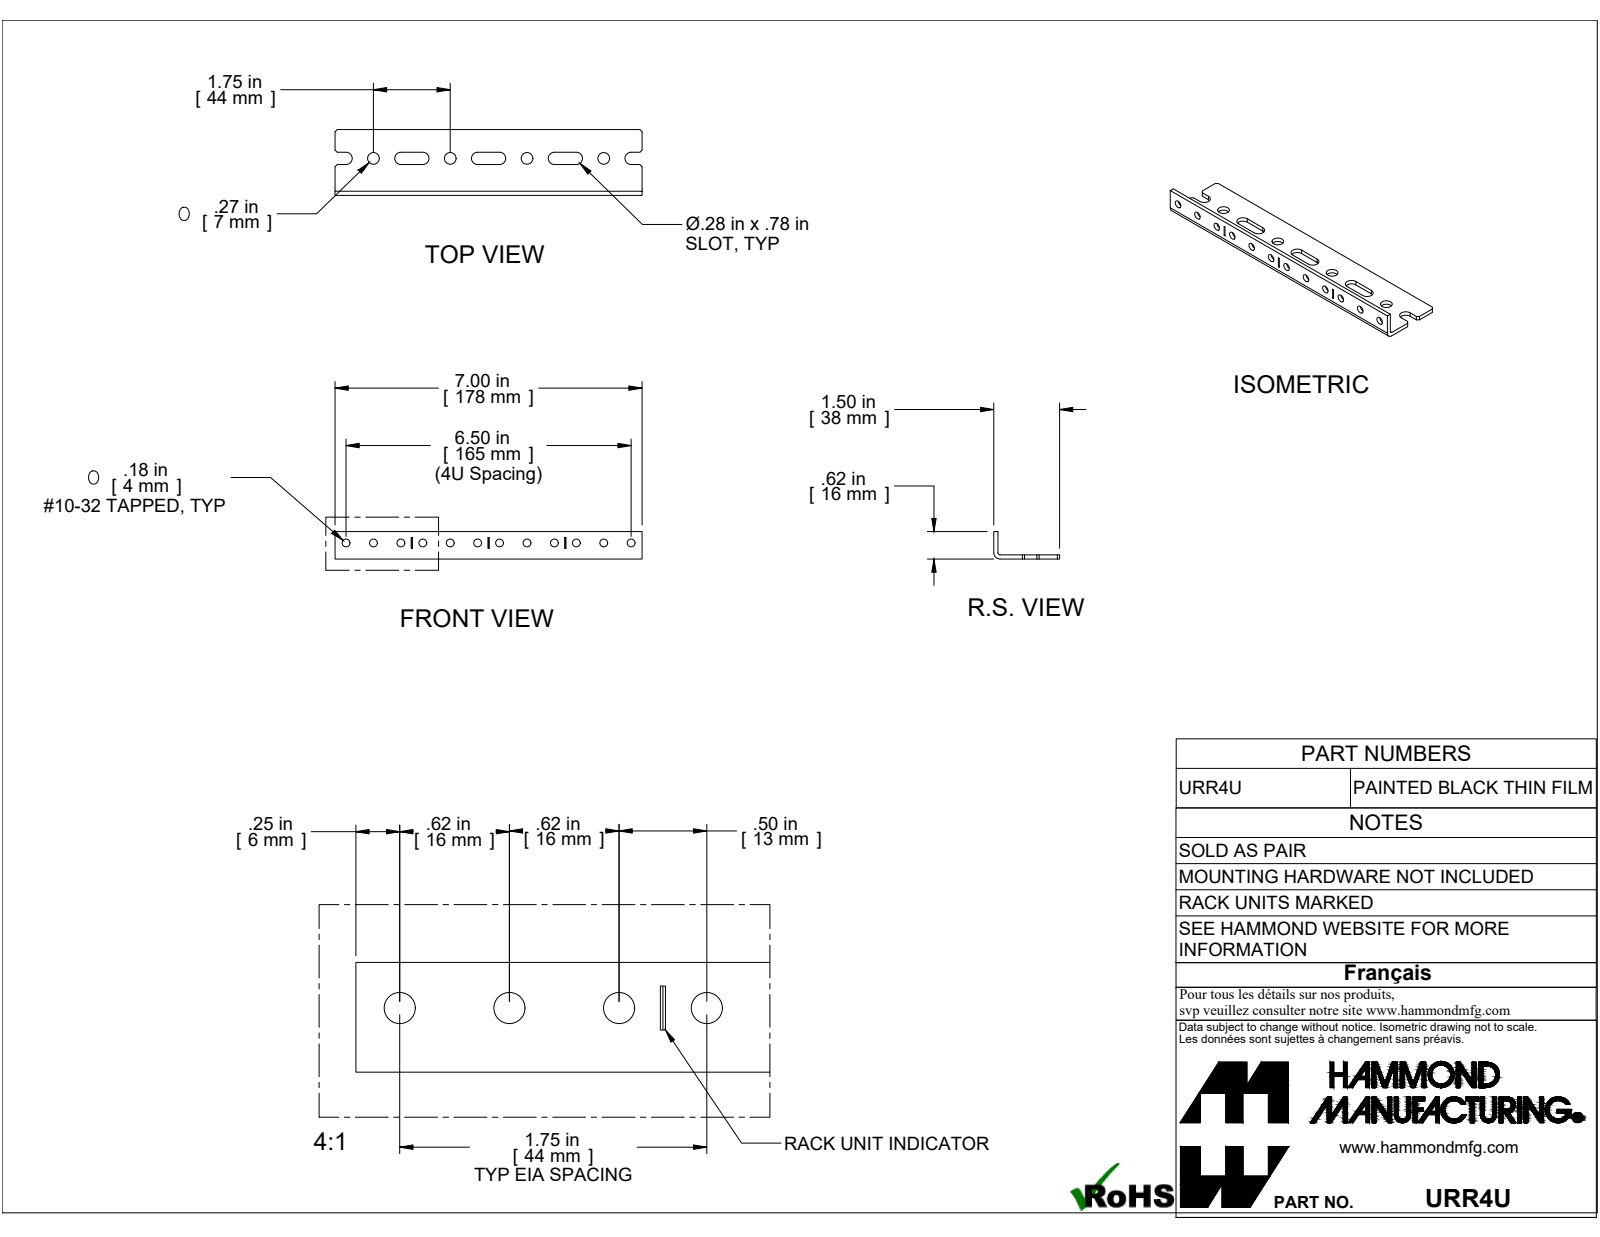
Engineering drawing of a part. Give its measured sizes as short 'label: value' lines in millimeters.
name: COM57213-4
written by: ST-DEVELOPER v16.7 (AUTOMOTIVE_DESIGN)
unit: mm
bodies: 1 solid, 64 faces (38 planar, 26 cylindrical, 0 other)
size: 177.8 × 38.1 × 15.88
volume: 19 592 mm³; area: 18 390 mm²
holes: 12× ⌀4.5, 4× ⌀6.76
rounds: 8× R3.57, 1× R1.22, 1× R3.63
face distances: 2.41, 15.88, 13.47, 38.1, 35.69, 17.84, 24.98, 15.43, 22.57, 7.14
hole spacings: 88.9, 44.45, 15.87, 15.88, 28.57, 31.75, 44.44, 60.32
